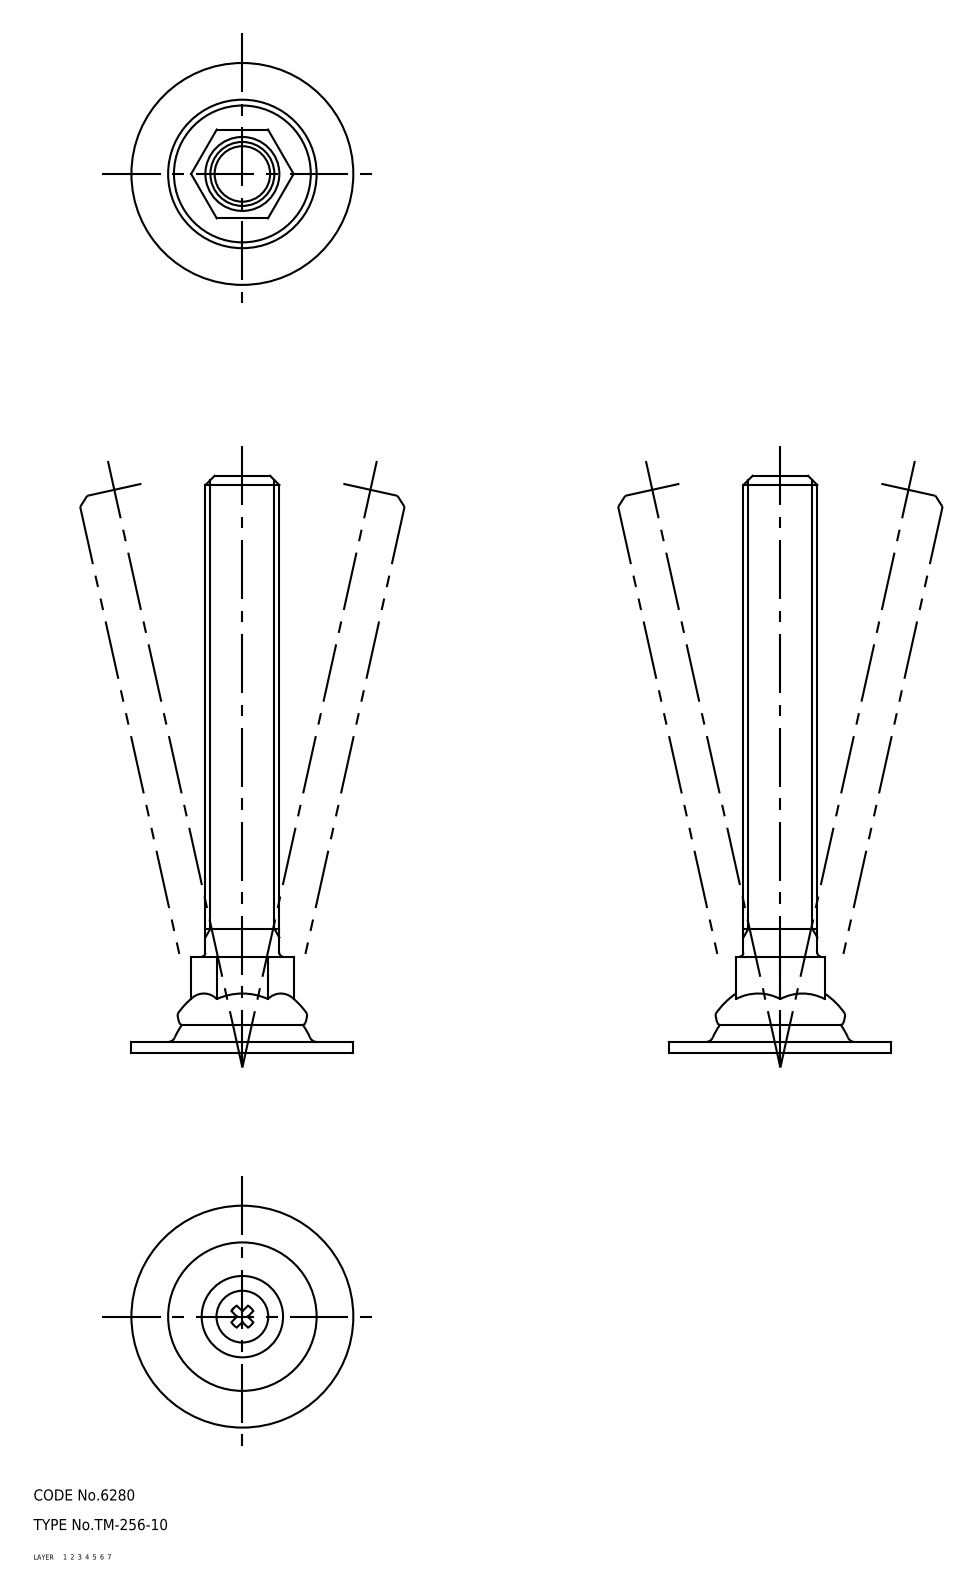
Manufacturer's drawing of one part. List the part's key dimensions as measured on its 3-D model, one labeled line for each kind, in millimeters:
Part name (STEP PRODUCT): 67113123; 67113136; 67113149; 67113162
STEP written by: CADfix (AUTOMOTIVE_DESIGN)
Units: millimetres
Bodies: 4 solids, 72 faces (0 planar, 0 cylindrical, 72 other)
Overall size (bounding box): 156 × 60 × 60
Volume: 58 220 mm³ · Surface area: 20 151 mm²
